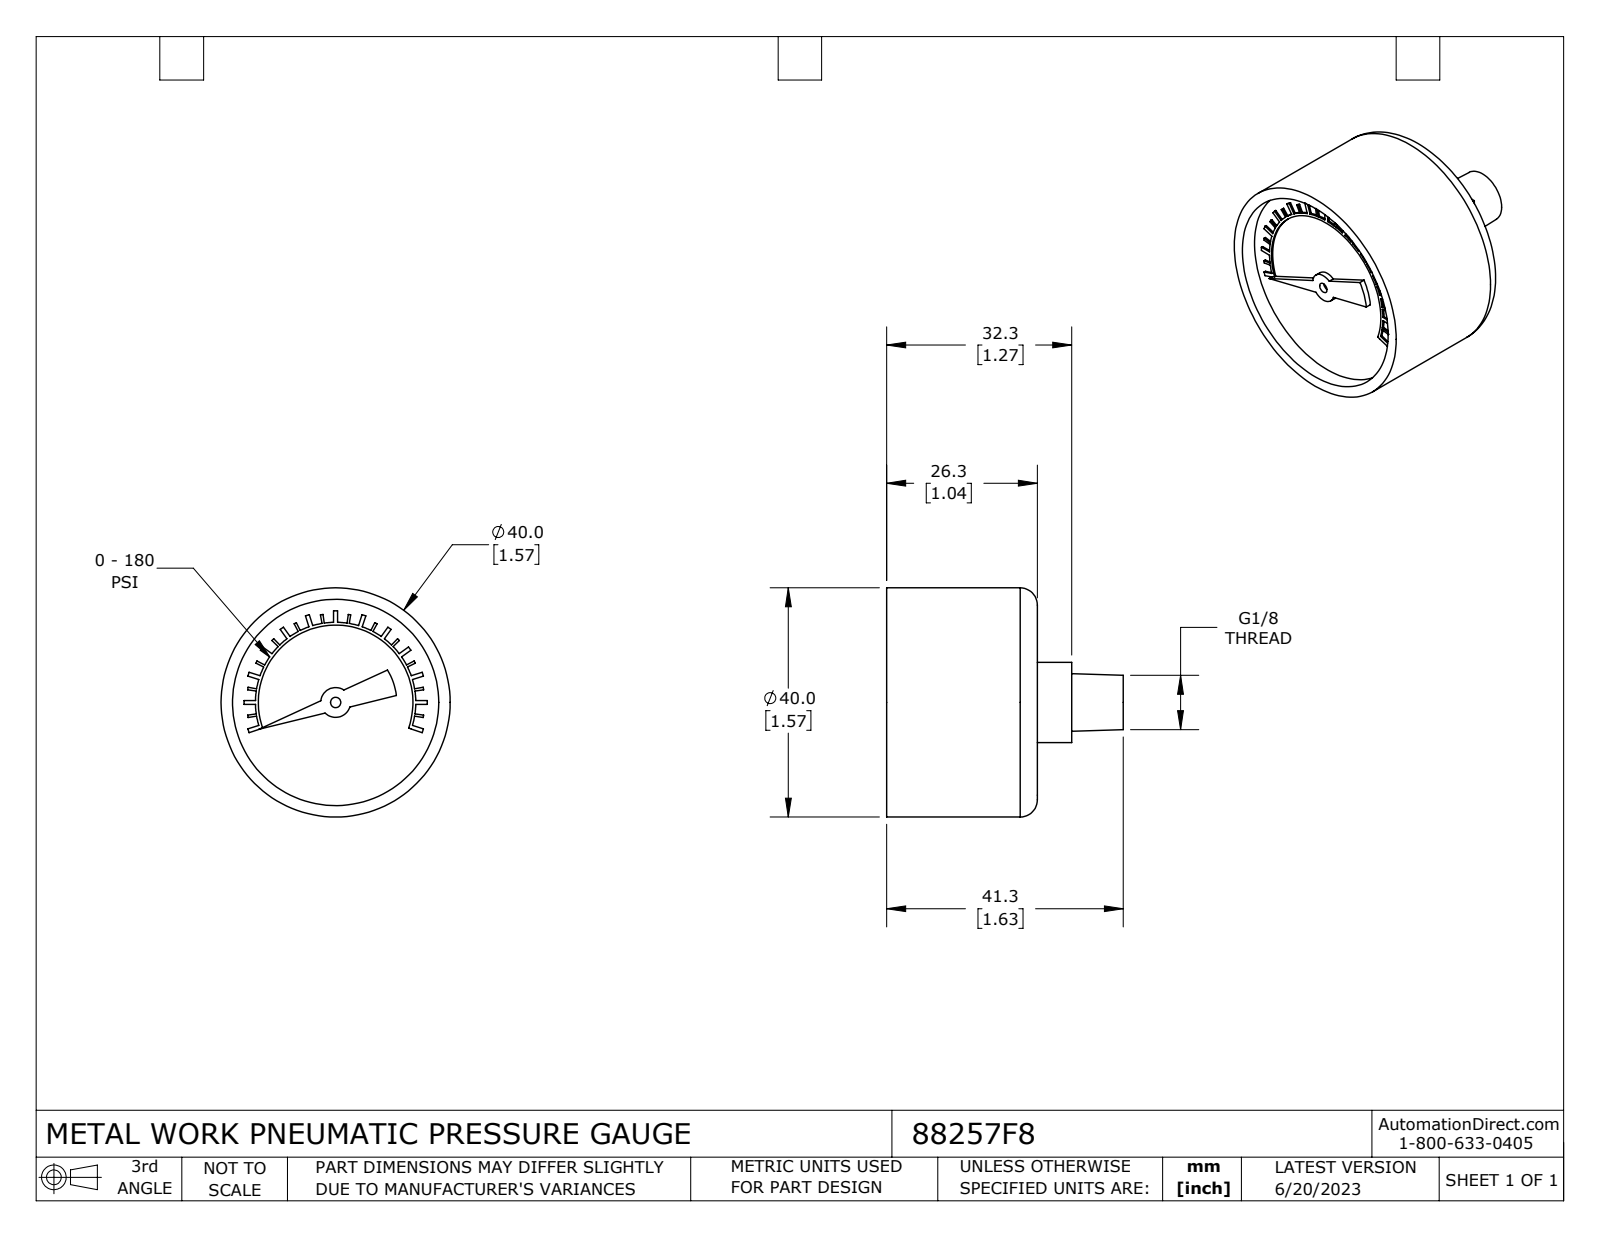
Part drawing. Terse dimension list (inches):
name: 88257F8
written by: SolidWorks 2021 (CONFIG_CONTROL_DESIGN)
unit: in
bodies: 1 solid, 133 faces (93 planar, 36 cylindrical, 4 other)
size: 1.626 × 1.575 × 1.575
volume: 1.934 in³; area: 10.41 in²
holes: 1× ⌀0.071, 1× ⌀1.417
bosses: 1× ⌀1.575
rounds: 1× R0.103, 1× R0.42, 1× R0.514, 1× R0.526, 1× R0.531, 1× R0.532, 1× R0.538, 1× R0.541
face distances: 0.917, 1.035, 0.118, 0.551, 0.236, 1.154, 1.272, 0.354, 0.591, 1.508
